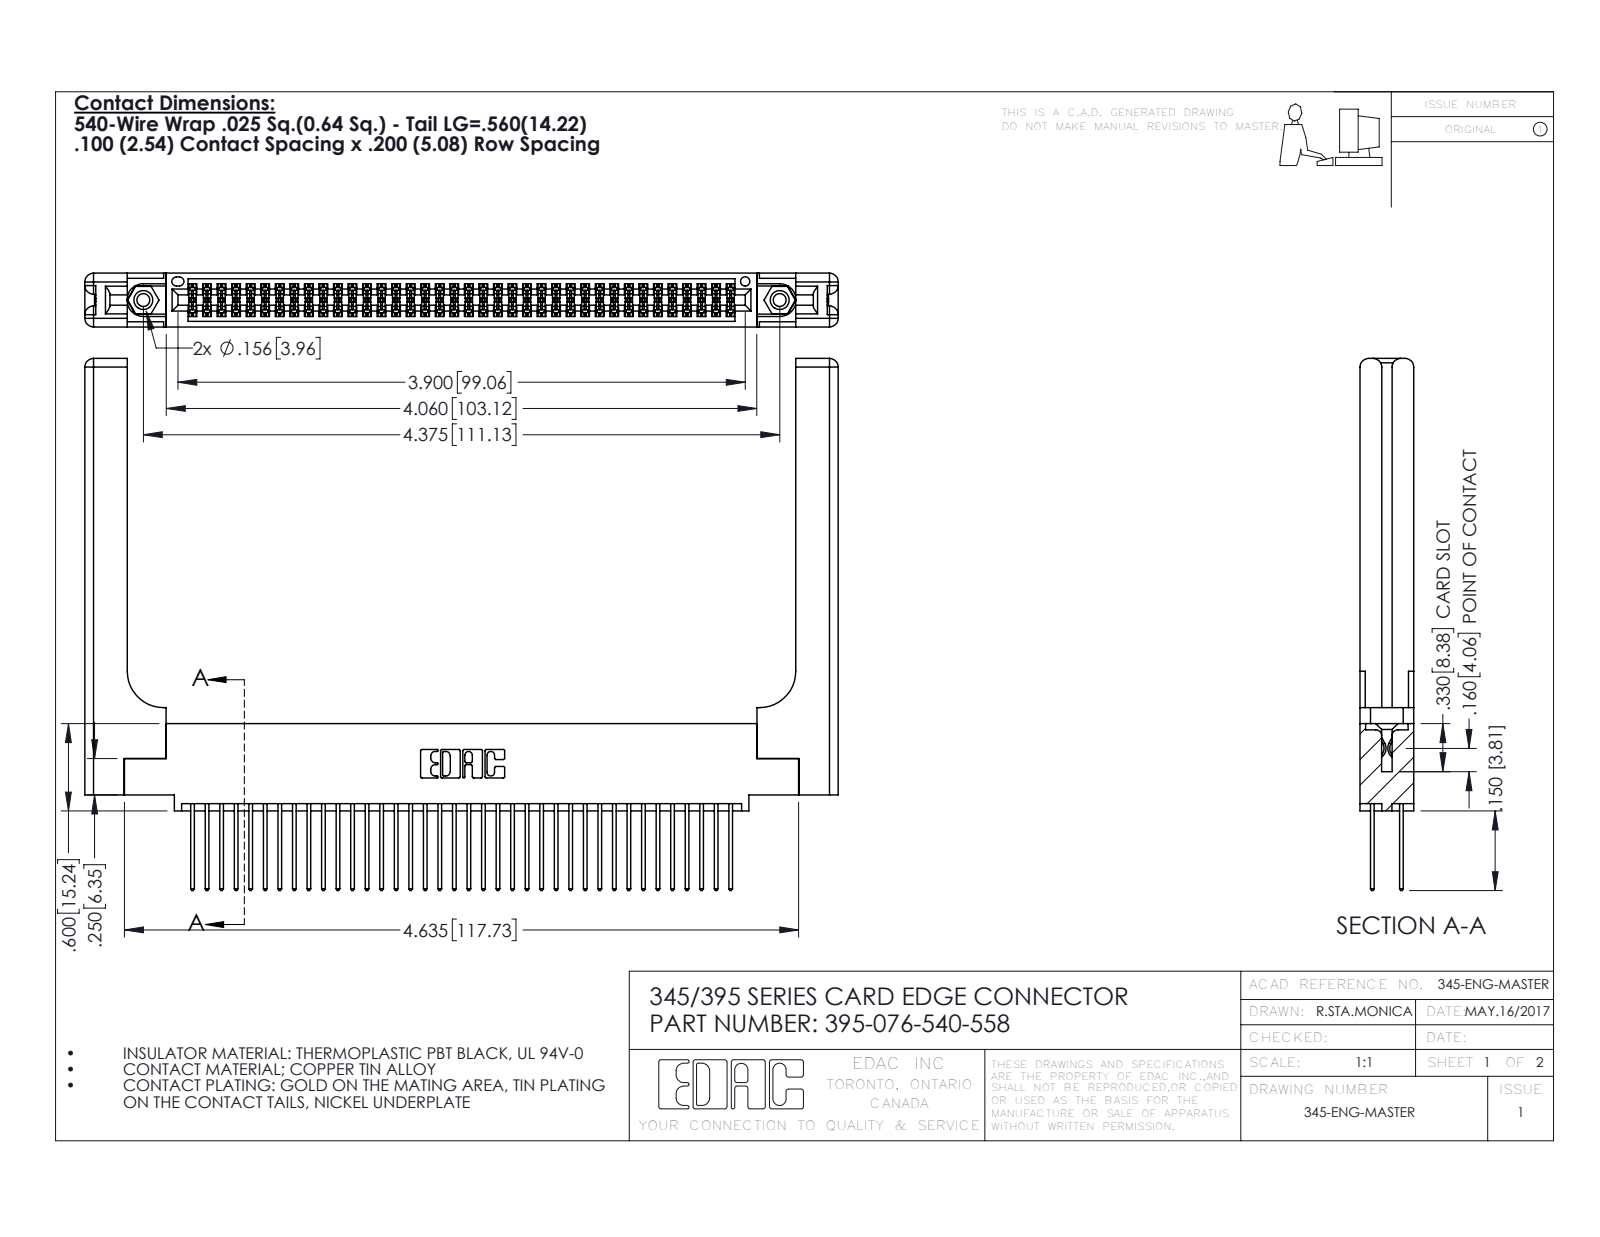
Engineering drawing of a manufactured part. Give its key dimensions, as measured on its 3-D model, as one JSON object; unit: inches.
{"part_name": "395-076-540-558; 345-250-001_345-250-001-102; 345 Part_0.110 Offset - 0.156 Dia-TH; 345-220-058_345-220-058 (+1 more)", "step_written_by": "SolidWorks 2016 (CONFIG_CONTROL_DESIGN)", "units": "inches", "bodies": {"solids": 81, "faces": 4186, "planar": 2740, "cylindrical": 1386, "other": 60}, "overall_size": [5.179, 3.657, 0.37], "volume_in3": 1.308, "surface_area_in2": 39.62, "round_holes": [[0.089, 2], [0.125, 2], [0.156, 2], [0.064, 1]], "round_bosses_or_shafts": [[0.155, 2]], "partial_cylinders_radius": [[0.006, 114], [0.01, 76], [0.01, 22], [0.06, 16], [0.007, 6], [0.031, 6], [0.026, 3], [0.014, 2]], "face_to_face_distances": [0.072, 0.298, 0.37, 0.098, 0.272, 0.025, 0.2, 0.225, 0.175, 0.148], "hole_center_spacings": [0.27, 4.139, 4.375]}
